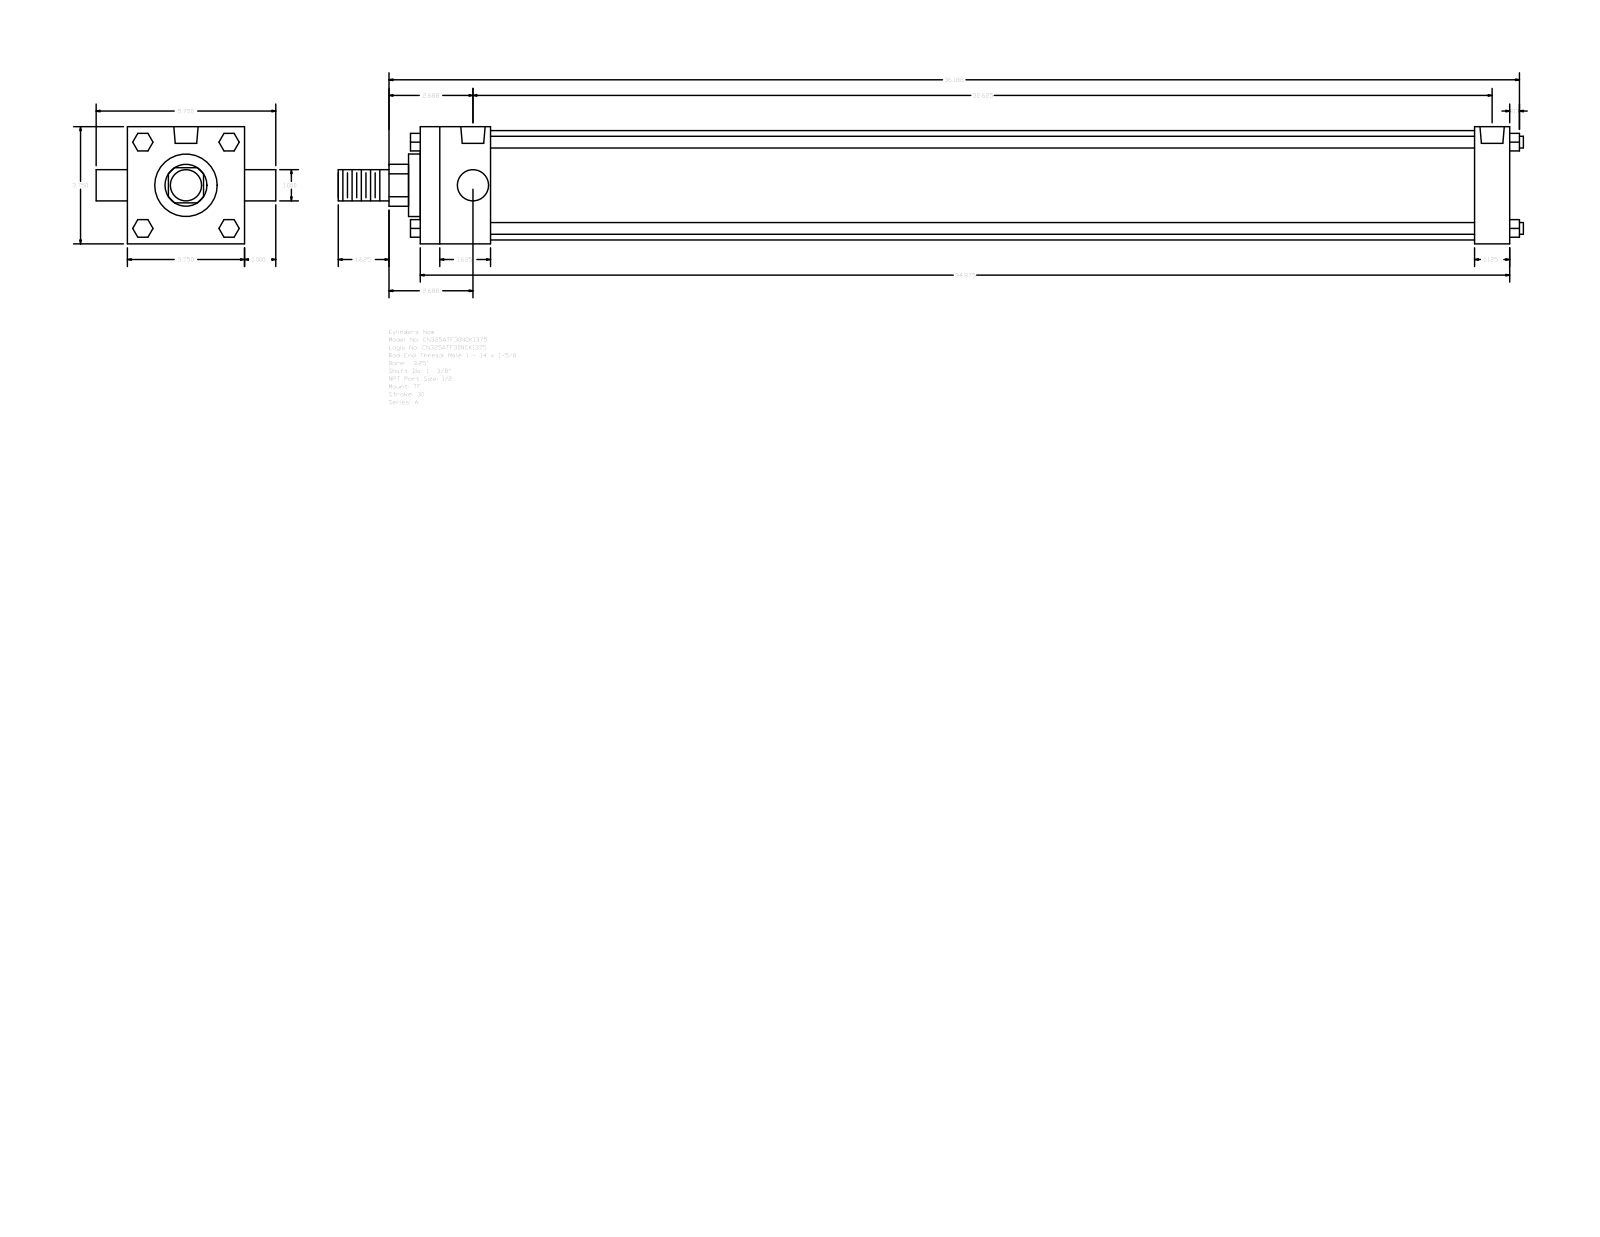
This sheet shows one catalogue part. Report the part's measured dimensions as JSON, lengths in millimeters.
{"part_name": "A_TF__0325_1.375", "step_written_by": "GSSL Pune (CONFIG_CONTROL_DESIGN)", "units": "millimeters", "bodies": {"solids": 0, "faces": 120, "planar": 92, "cylindrical": 28, "other": 0}, "overall_size": [963.61, 146.05, 95.25], "round_holes": [[8.73, 3], [19.77, 2]], "round_bosses_or_shafts": [[9.53, 4], [25.4, 2], [88.9, 1], [50.8, 1], [34.92, 1]], "partial_cylinders_radius": [[17.06, 1]], "face_to_face_distances": [95.24, 885.83, 57.15, 28.58, 857.25, 800.1, 828.68, 66.67, 9.52, 866.77], "hole_center_spacings": [3.18, 825.5, 822.32, 828.68]}
